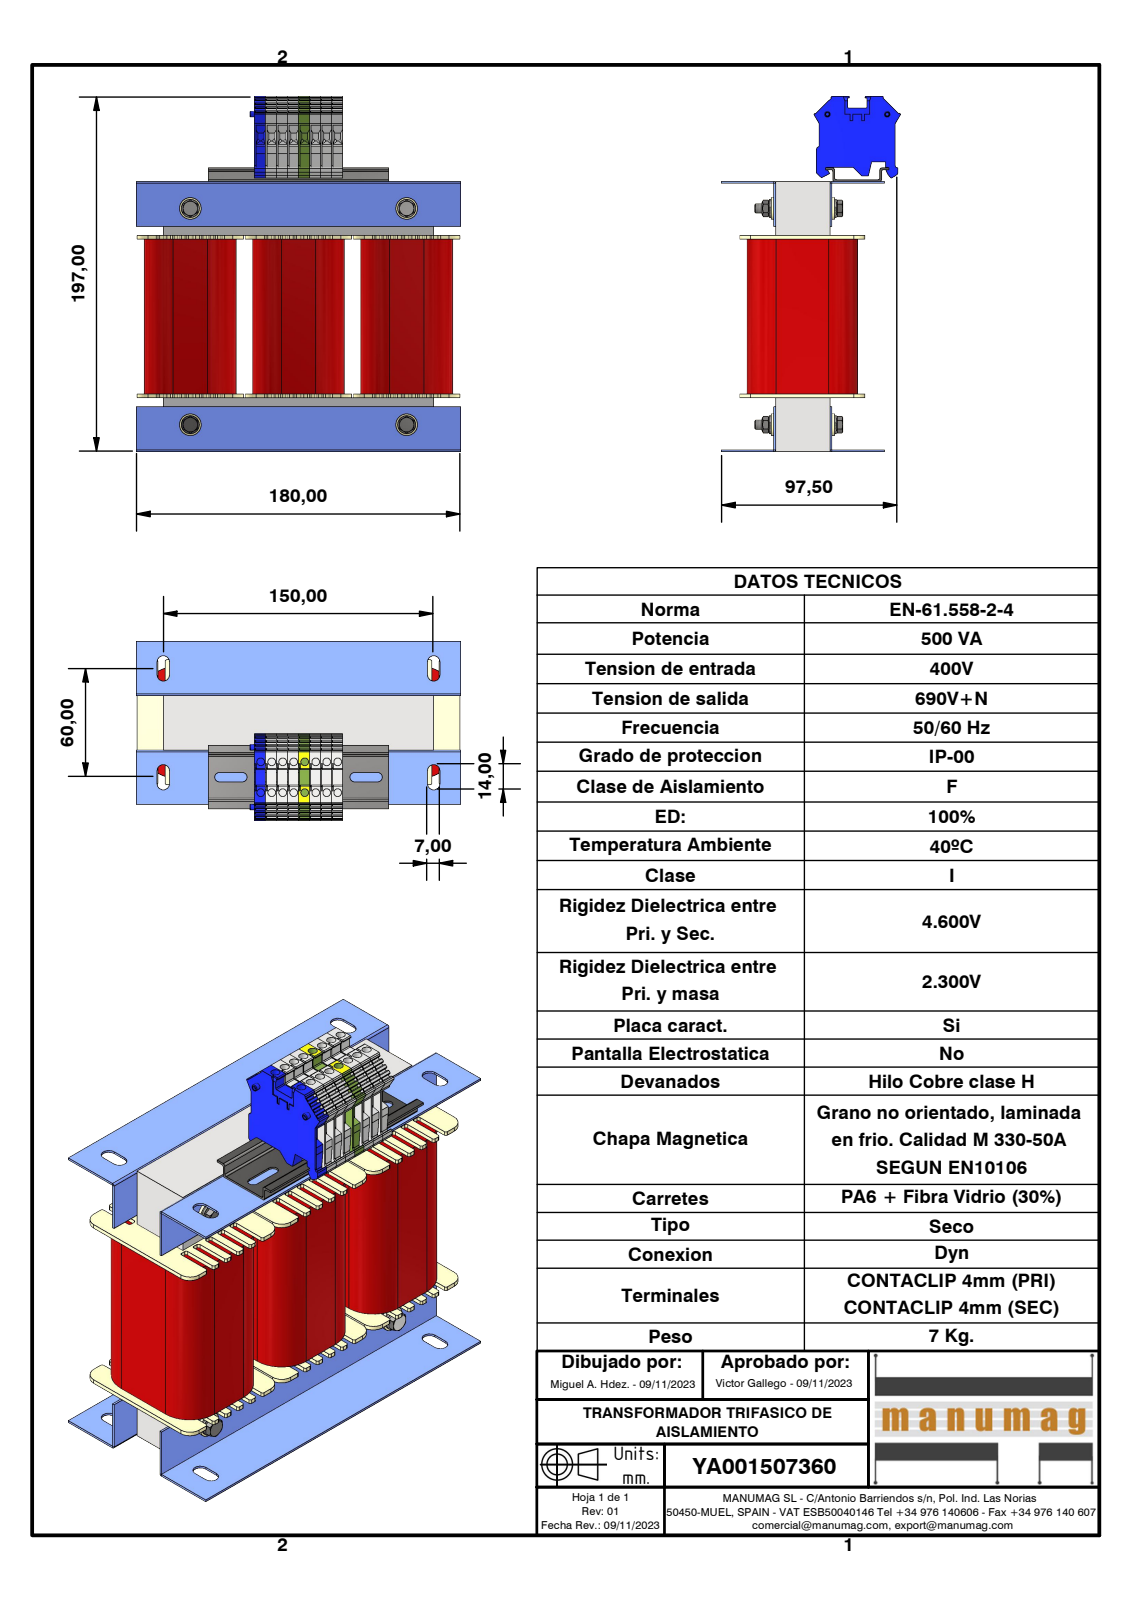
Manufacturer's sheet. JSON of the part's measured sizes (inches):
{"part_name": "YA001507360; 3UI90 150 x 150 - 30 (Rc30); UI 90_30; RC30 NT030 (+8 more)", "step_written_by": "Autodesk Inventor 2023 (AUTOMOTIVE_DESIGN)", "units": "inches", "bodies": {"solids": 41, "faces": 3082, "planar": 2178, "cylindrical": 736, "other": 168}, "overall_size": [7.766, 7.087, 3.899], "volume_in3": 71.15, "surface_area_in2": 498.6, "round_holes": [[0.169, 16], [0.163, 4], [0.197, 4], [0.209, 4], [0.236, 4], [0.413, 4], [0.094, 2], [0.098, 2], [0.108, 2], [0.116, 2]], "round_bosses_or_shafts": [[0.472, 4], [0.394, 4], [0.264, 4], [0.232, 4], [0.18, 4]], "partial_cylinders_radius": [[0.039, 132], [0.01, 16], [0.236, 12], [0.63, 12], [0.102, 8], [0.138, 8], [0.012, 5], [0.02, 5]], "face_to_face_distances": [1.181, 0.039, 4.724, 2.362, 1.22, 3.543, 5.906, 5.866, 4.685, 0.24], "hole_center_spacings": [0.24, 0.711, 0.48, 0.824, 0.72, 0.983, 0.669, 0.961]}
